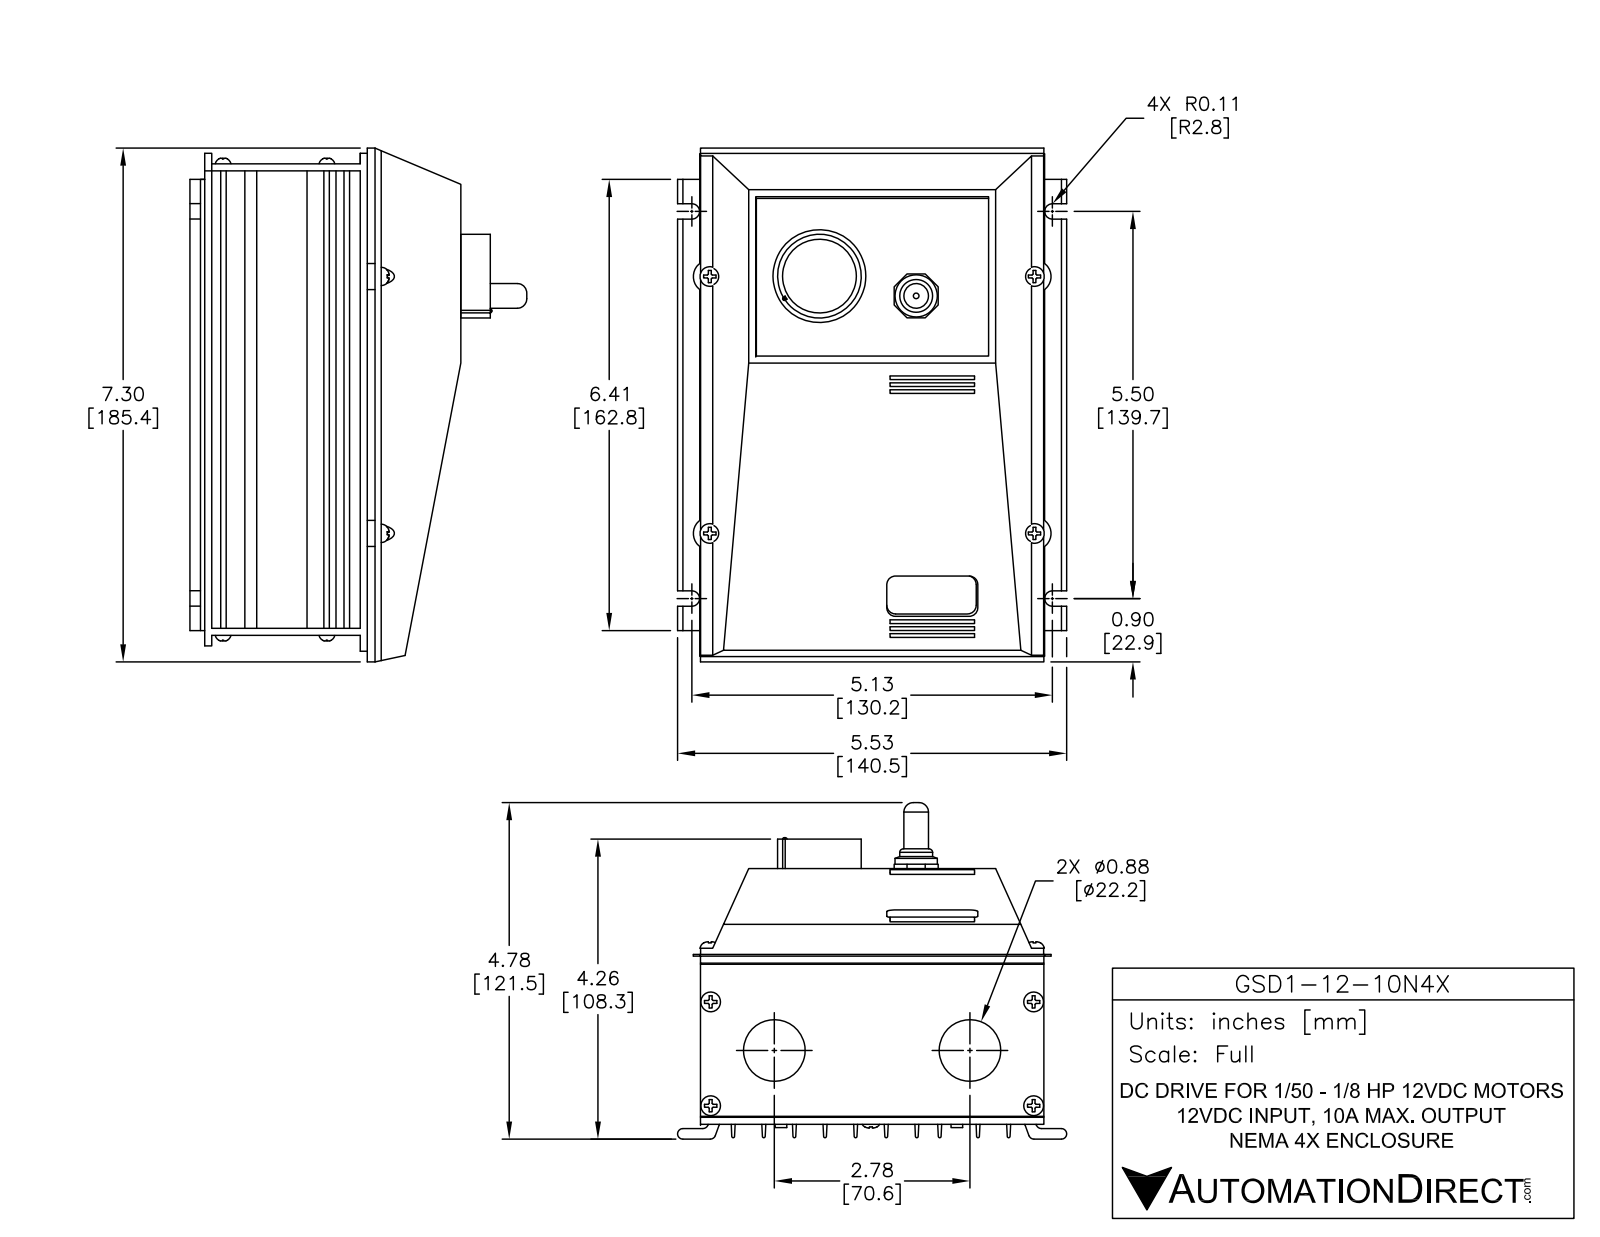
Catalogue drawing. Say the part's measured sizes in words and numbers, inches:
The part is named "HDS6P7; SW4 Nut; TH_T-BLK_9POS_5S-45L-10.2W-14.5H; BK700B (+8 more)". Its 3-D file was written by "SolidWorks 2014 (AUTOMOTIVE_DESIGN)". It is 77 solids with 4005 faces: 2437 planar, 1171 cylindrical and 397 other. Overall it measures 7.3 by 5.53 by 4.782 inches. Its volume is 28.43 cubic inches and its surface area 577 square inches. Round holes: 15 of diameter 0.046, 14 of diameter 0.033, 14 of diameter 0.04, 10 of diameter 0.11, 10 of diameter 0.14, 9 of diameter 0.055, 9 of diameter 0.157, 4 of diameter 0.043, 4 of diameter 0.111, 4 of diameter 0.113, 4 of diameter 0.13, 4 of diameter 0.17. Round bosses or shafts: 14 of diameter 0.134, 13 of diameter 0.038, 5 of diameter 0.118, 4 of diameter 0.318, 4 of diameter 0.164, 4 of diameter 0.163, 4 of diameter 0.137, 4 of diameter 0.13. Partial cylindrical surfaces (rounded edges, fillets, slot ends): 56 of radius 0.025, 29 of radius 0.02, 13 of radius 0.125, 12 of radius 0.05, 12 of radius 0.075, 11 of radius 0.04, 8 of radius 0.094, 6 of radius 0.035. The main face-to-face distances are 0.1, 0.15, 0.25, 0.08, 0.35, 3.321, 0.5, 2.35, 2.1, 3.571. The hole center spacings are 0.5, 0.55, 1.1, 1.65, 0.155, 0.185, 0.4, 0.405.
